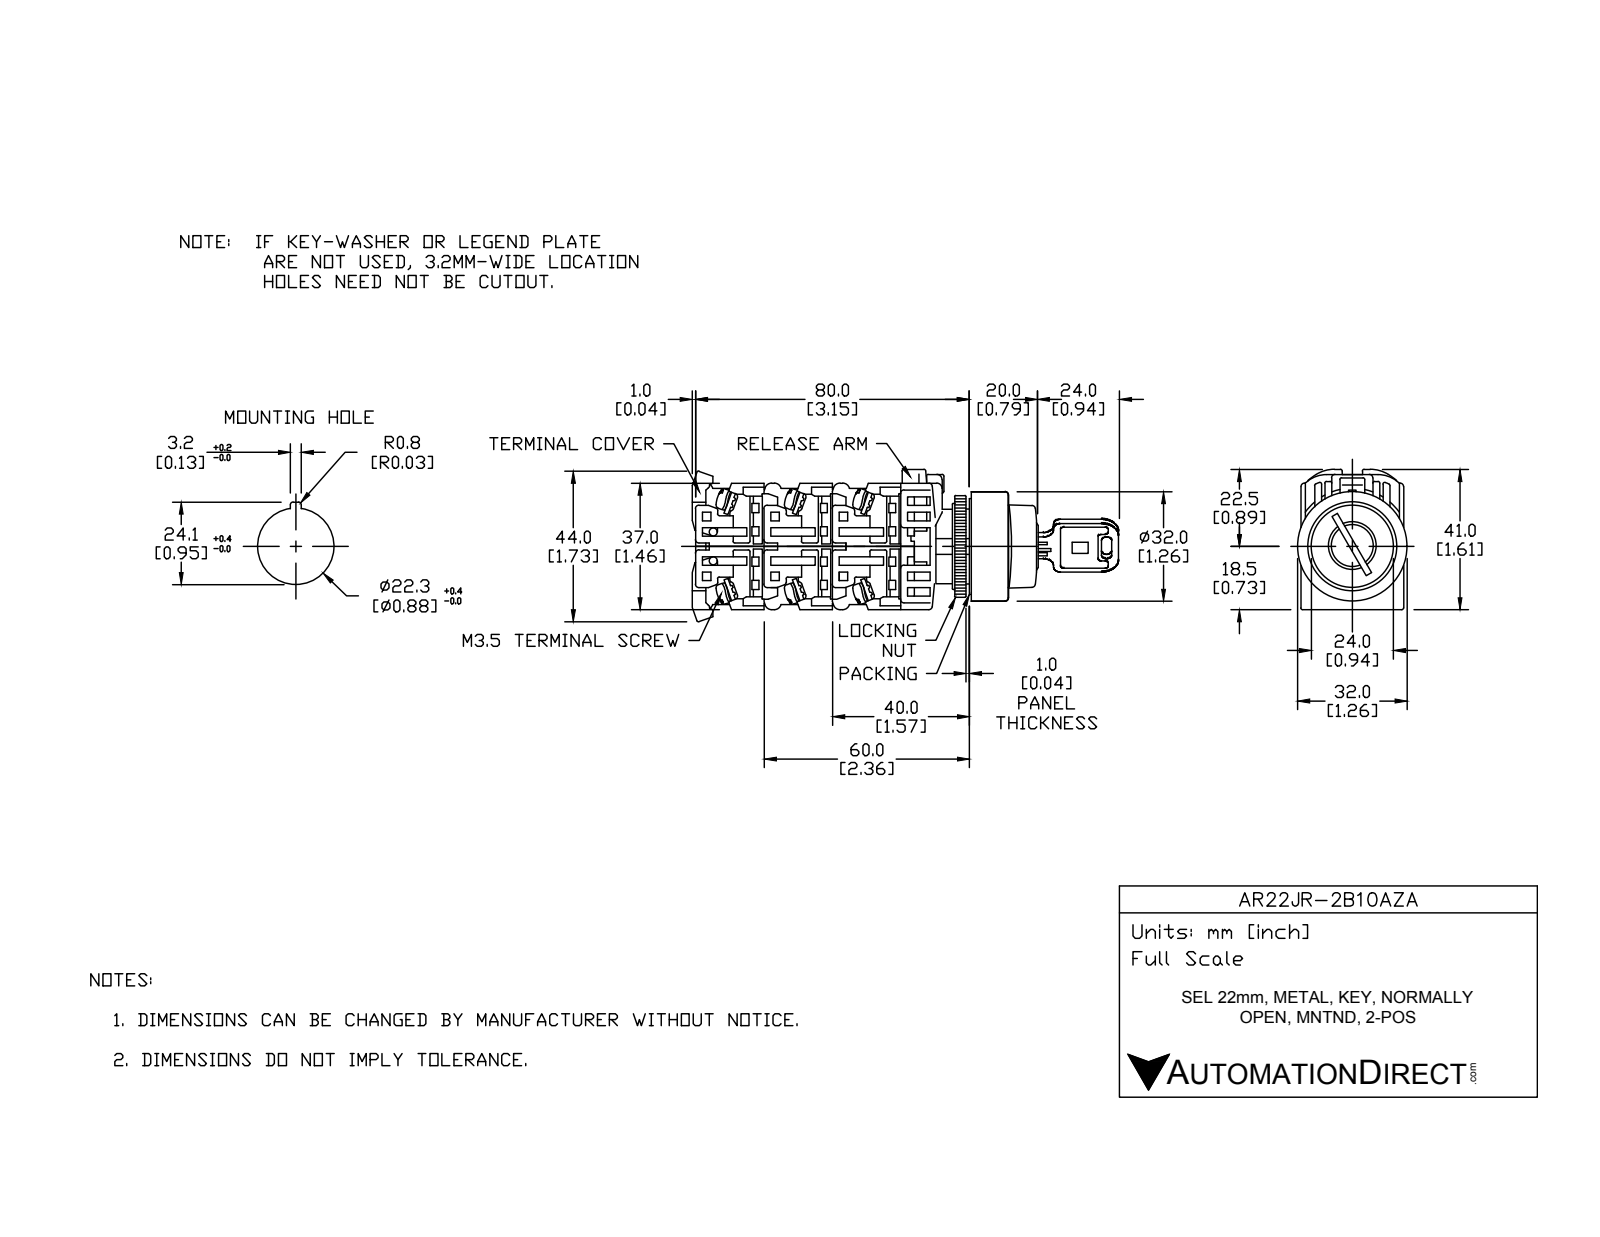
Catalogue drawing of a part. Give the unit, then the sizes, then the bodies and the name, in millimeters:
Units: millimetres
Overall size (bounding box): 61.5 × 41 × 32
Round holes (diameter × count): ⌀14 ×1, ⌀21.8 ×1, ⌀22 ×1, ⌀25 ×1, ⌀31 ×1
Round bosses / shafts (diameter × count): ⌀5 ×2, ⌀32 ×1, ⌀30.5 ×1, ⌀29.8 ×1, ⌀24 ×1, ⌀21.75 ×1, ⌀17 ×1, ⌀13.8 ×1
Partial cylindrical surfaces — rounded edges, fillets, slot ends (radius × count): R0.5 ×23, R1.75 ×4, R5 ×4, R4 ×2, R16.59 ×1, R17.59 ×1
Main face-to-face distances: 1, 28.5, 20, 2, 18, 3, 29, 40.5, 23, 30
Volume: 31 000 mm³ · Surface area: 21 257 mm²
Bodies: 13 solids, 308 faces (208 planar, 78 cylindrical, 22 other)
Part name (STEP PRODUCT): AR22JR-2B10AZA
STEP written by: SolidWorks 2017 (AUTOMOTIVE_DESIGN)
